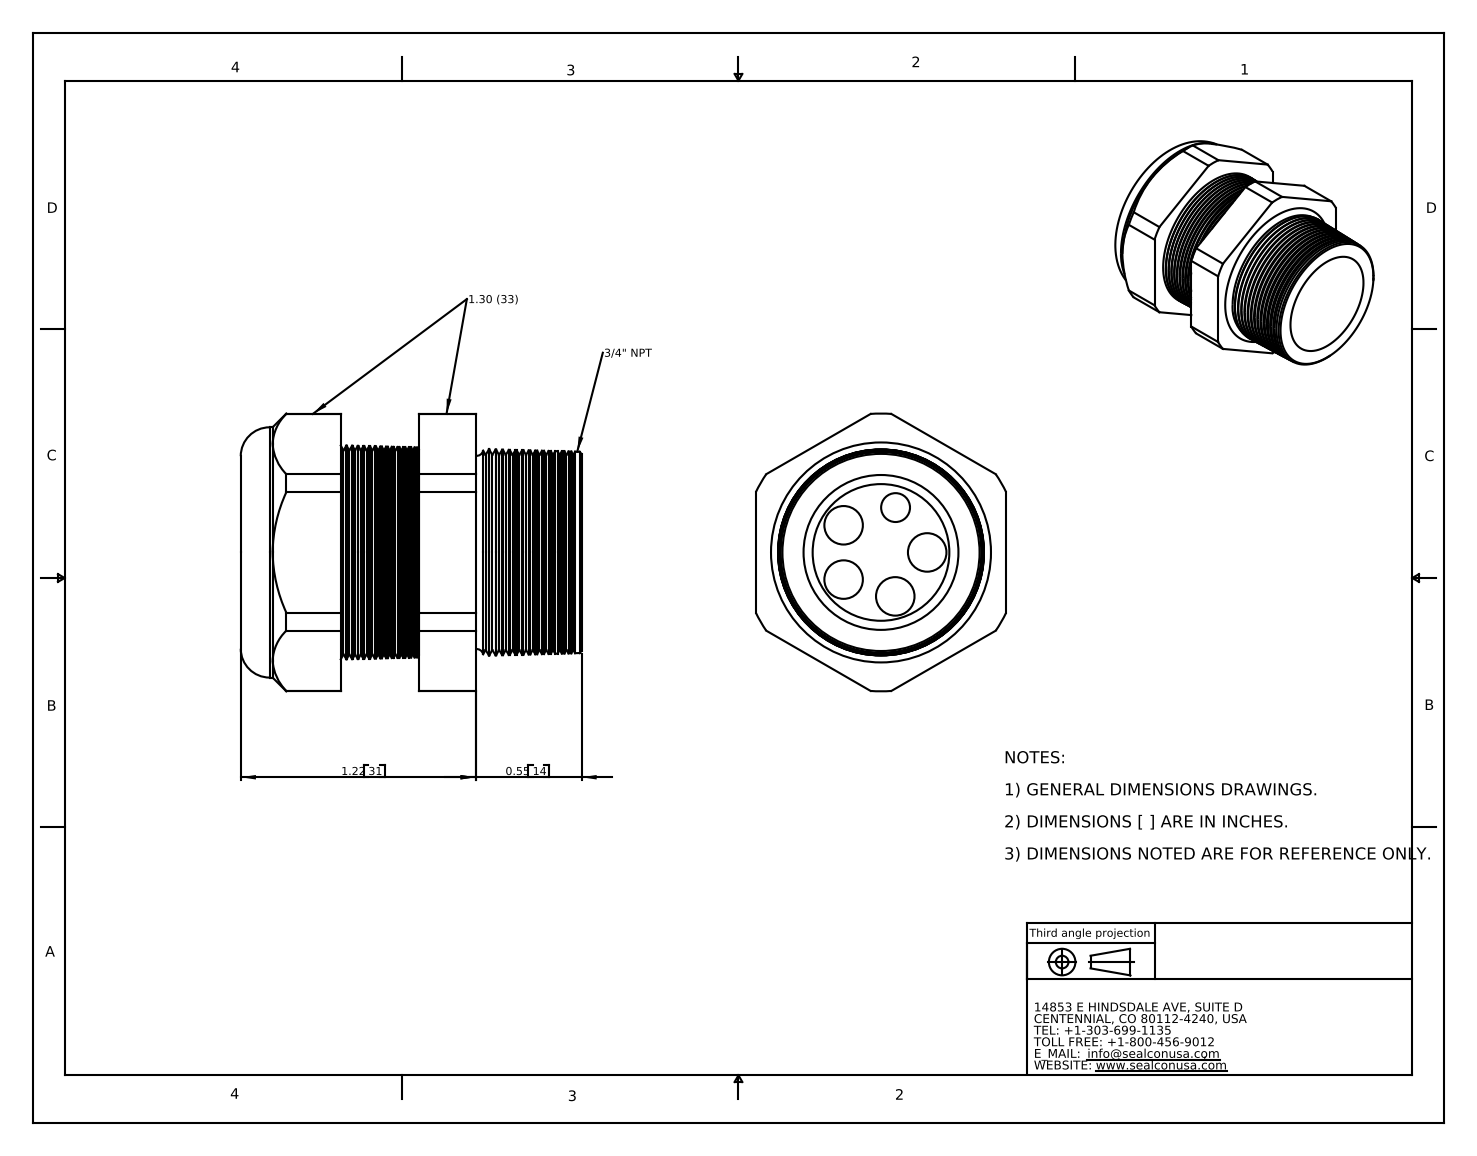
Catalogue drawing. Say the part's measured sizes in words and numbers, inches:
The part is named "CD21N8-BK". Its 3-D file was written by "SolidWorks 2007 (CONFIG_CONTROL_DESIGN)". It is 2 solids with 234 faces: 20 planar, 30 cylindrical and 184 other. Overall it measures 1.77 by 1.443 by 1.3 inches. Its volume is 1.29 cubic inches and its surface area 18.38 square inches. Round holes: 4 of diameter 0.2, 1 of diameter 0.15, 1 of diameter 0.69, 1 of diameter 0.71. Round bosses or shafts: 1 of diameter 1.3. Partial cylindrical surfaces (rounded edges, fillets, slot ends): 1 of radius 0.721. The main face-to-face distances are 1.3, 0.405, 0.7, 0.295, 0.52, 0.925, 1.22, 1.77, 1.25, 0.845. The hole center spacings are 0.24, 0.24, 0.282, 0.457, 0.245, 0.282, 0.285, 0.285.
